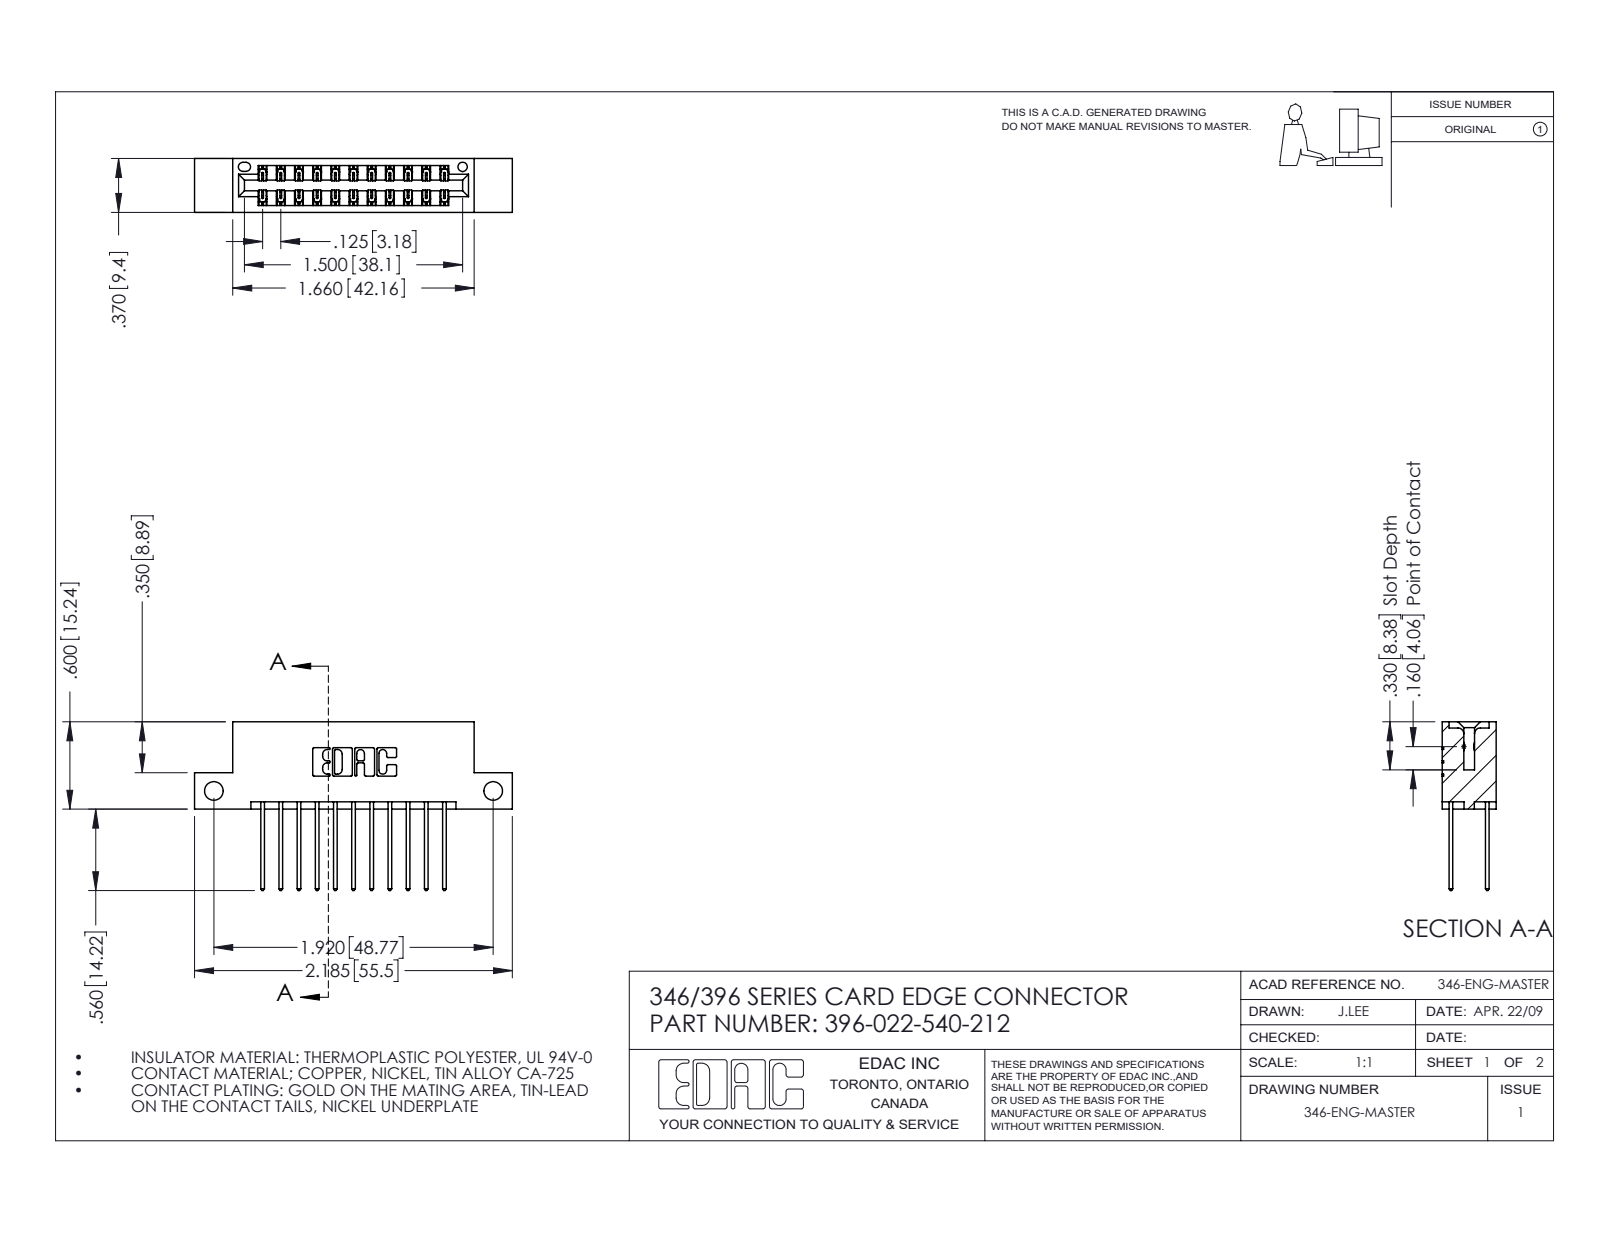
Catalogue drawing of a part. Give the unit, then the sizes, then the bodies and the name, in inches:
Units: inches
Overall size (bounding box): 2.185 × 1.16 × 0.37
Round holes (diameter × count): ⌀0.128 ×2, ⌀0.064 ×1
Partial cylindrical surfaces — rounded edges, fillets, slot ends (radius × count): R0.006 ×33, R0.01 ×22, R0.01 ×22, R0.007 ×6, R0.031 ×6, R0.026 ×3, R0.014 ×2, R0.022 ×2
Main face-to-face distances: 0.25, 0.048, 0.322, 0.37, 0.072, 0.298, 0.025, 0.275, 0.148, 0.222
Hole centre spacings: 1.92
Volume: 0.315 in³ · Surface area: 10.65 in²
Bodies: 23 solids, 1266 faces (846 planar, 420 cylindrical, 0 other)
Part name (STEP PRODUCT): 346 Part_Flush Mounting Lugs - Side Mount; 345-292-001_345-293-140; 396-022-540-212
STEP written by: SolidWorks 2016 (CONFIG_CONTROL_DESIGN)
